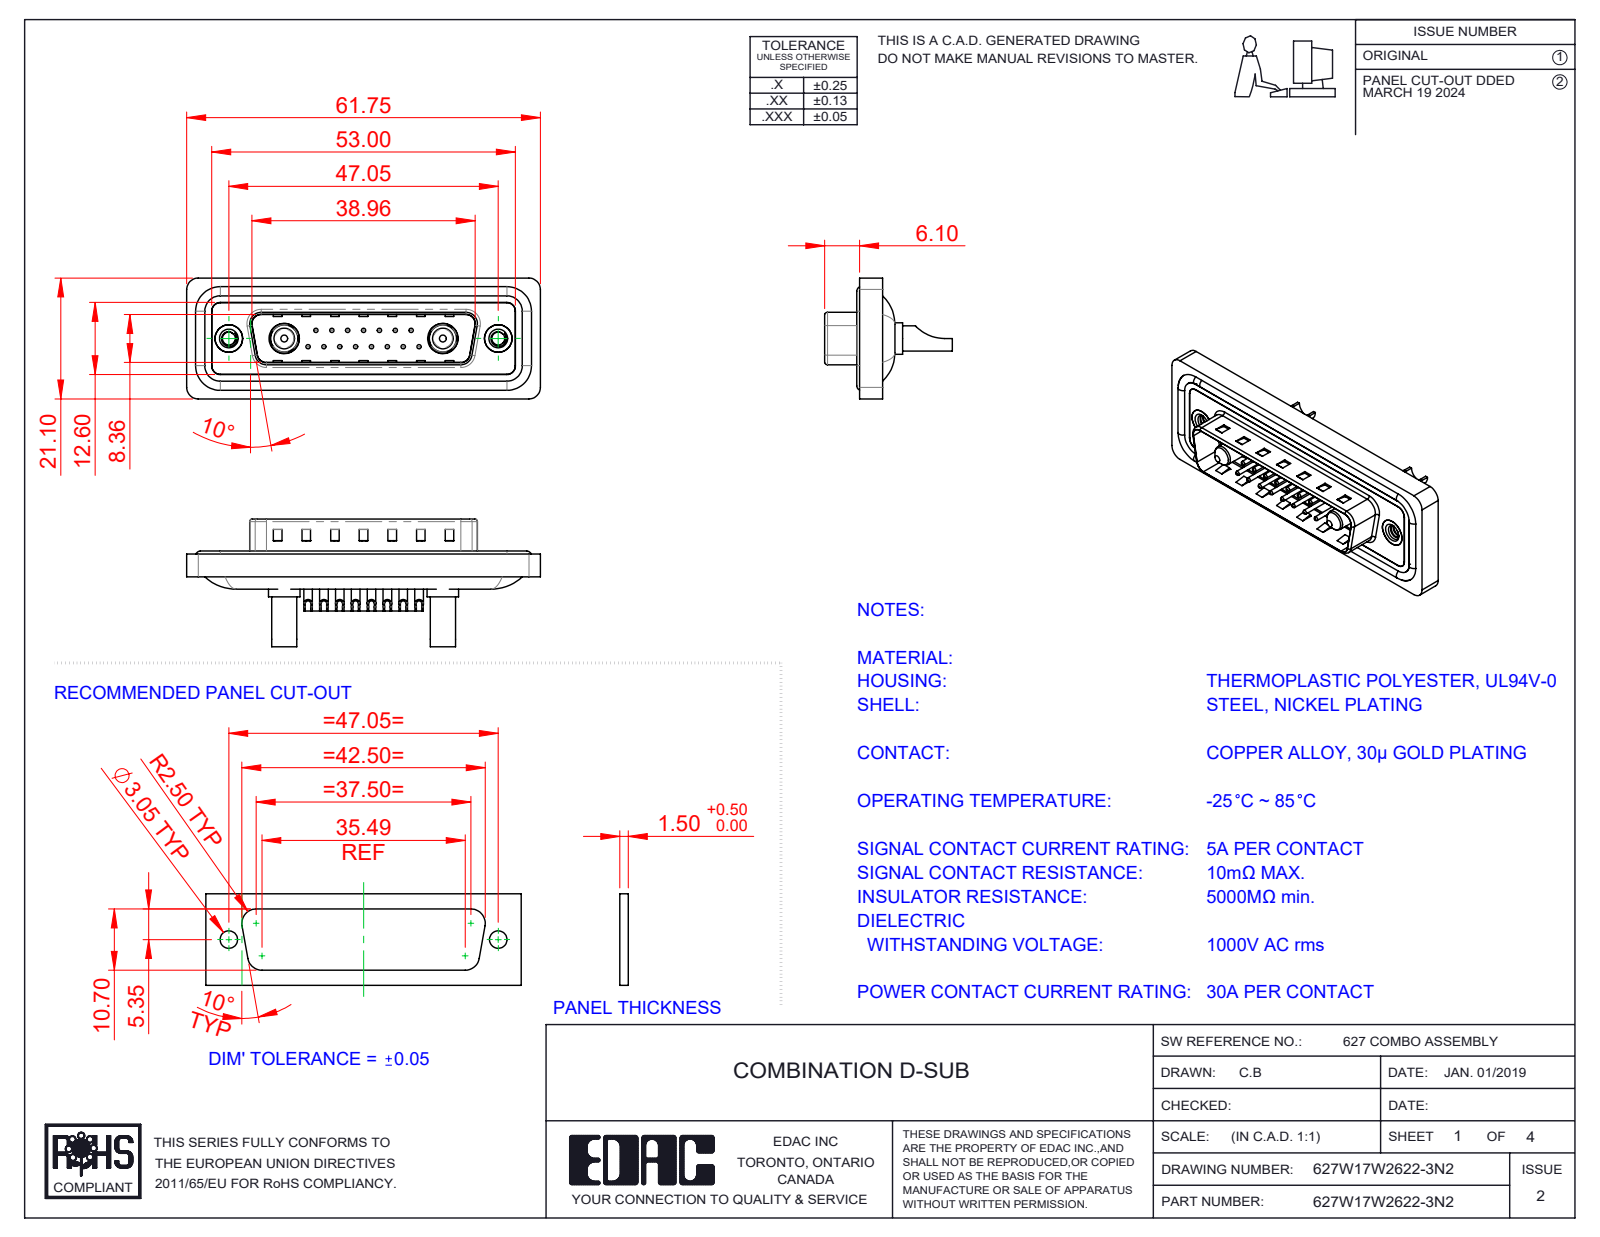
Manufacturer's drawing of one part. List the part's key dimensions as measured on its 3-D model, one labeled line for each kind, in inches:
Part name (STEP PRODUCT): 627Combo Contact Row 1_22; 627Combo Shell Rear_25 Contacts; Power Pin_30A SC; 627Combo Housing_17W2 (+5 more)
STEP written by: SolidWorks 2023 (CONFIG_CONTROL_DESIGN)
Units: inches
Bodies: 26 solids, 1128 faces (370 planar, 472 cylindrical, 286 other)
Overall size (bounding box): 2.431 × 0.878 × 0.831
Volume: 0.448 in³ · Surface area: 18.98 in²
Round holes (diameter × count): ⌀0.03 ×15, ⌀0.039 ×15, ⌀0.063 ×15, ⌀0.079 ×15, ⌀0.089 ×2, ⌀0.138 ×2, ⌀0.157 ×2, ⌀0.189 ×2, ⌀0.191 ×2, ⌀0.197 ×2, ⌀0.209 ×2
Round bosses / shafts (diameter × count): ⌀0.059 ×15, ⌀0.063 ×4, ⌀0.217 ×2, ⌀0.205 ×2, ⌀0.193 ×2, ⌀0.187 ×2, ⌀0.173 ×2, ⌀0.148 ×2
Partial cylindrical surfaces — rounded edges, fillets, slot ends (radius × count): R0.059 ×22, R0.079 ×18, R0.02 ×8, R0.063 ×8, R0.039 ×6, R0.01 ×4, R0.024 ×4, R0.026 ×4
Main face-to-face distances: 0.016, 0.059, 0.043, 0.063, 0.02, 0.122, 0.114, 0.032, 0.377, 0.161
Hole centre spacings: 0.124, 0.109, 0.218, 0.327, 0.198, 0.295, 0.436, 0.198
